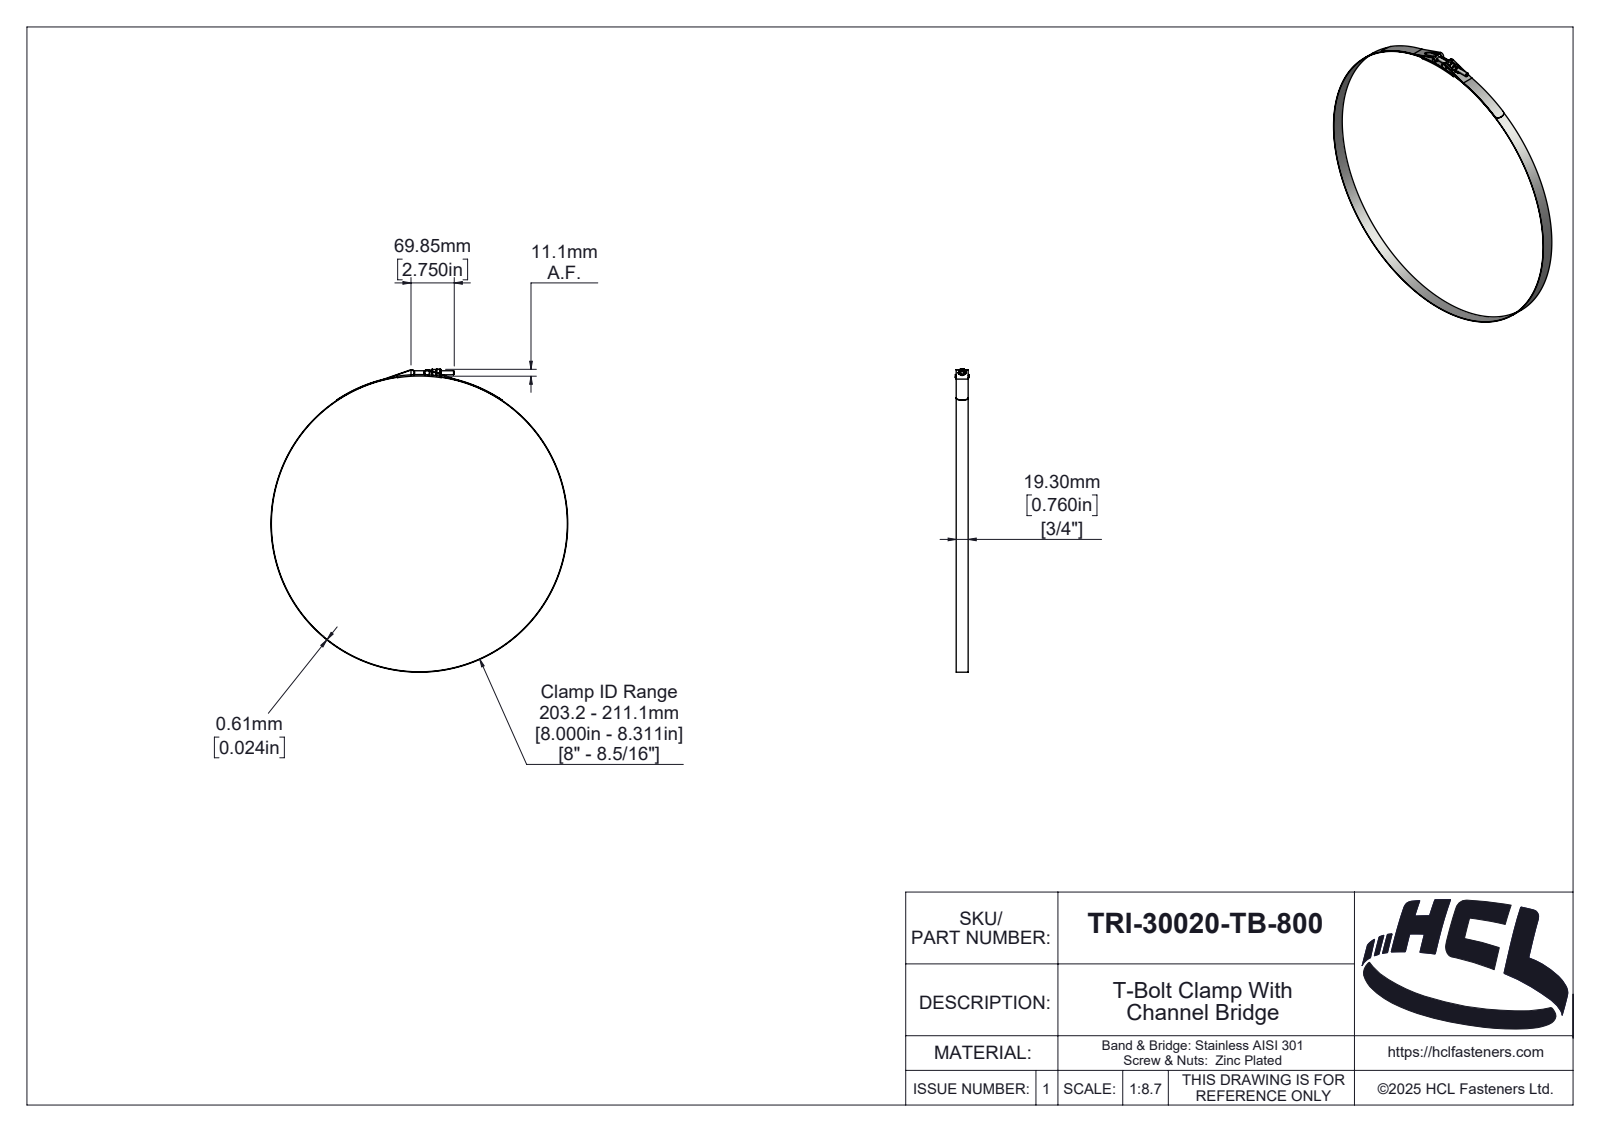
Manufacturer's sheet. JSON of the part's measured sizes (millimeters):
{"part_name": "TRI-30020-TB-800", "step_written_by": "SolidWorks 2025 (AUTOMOTIVE_DESIGN)", "units": "millimeters", "bodies": {"solids": 6, "faces": 330, "planar": 44, "cylindrical": 122, "other": 164}, "overall_size": [489.01, 479.22, 22], "volume_mm3": 25598, "surface_area_mm2": 76961, "round_holes": [[5.4, 1], [6.35, 1], [6.5, 1], [7.58, 1], [478, 1]], "round_bosses_or_shafts": [[8.58, 2], [479.22, 1], [10.58, 1]], "partial_cylinders_radius": [[0.39, 6], [0.5, 2], [4.39, 2], [5, 2], [0.59, 1], [2.42, 1], [3.03, 1], [3.19, 1]], "face_to_face_distances": [0.61, 19.3, 1.35, 20.65, 0.74, 21.39, 20.04, 22, 20.78, 11.12], "hole_center_spacings": [244]}
